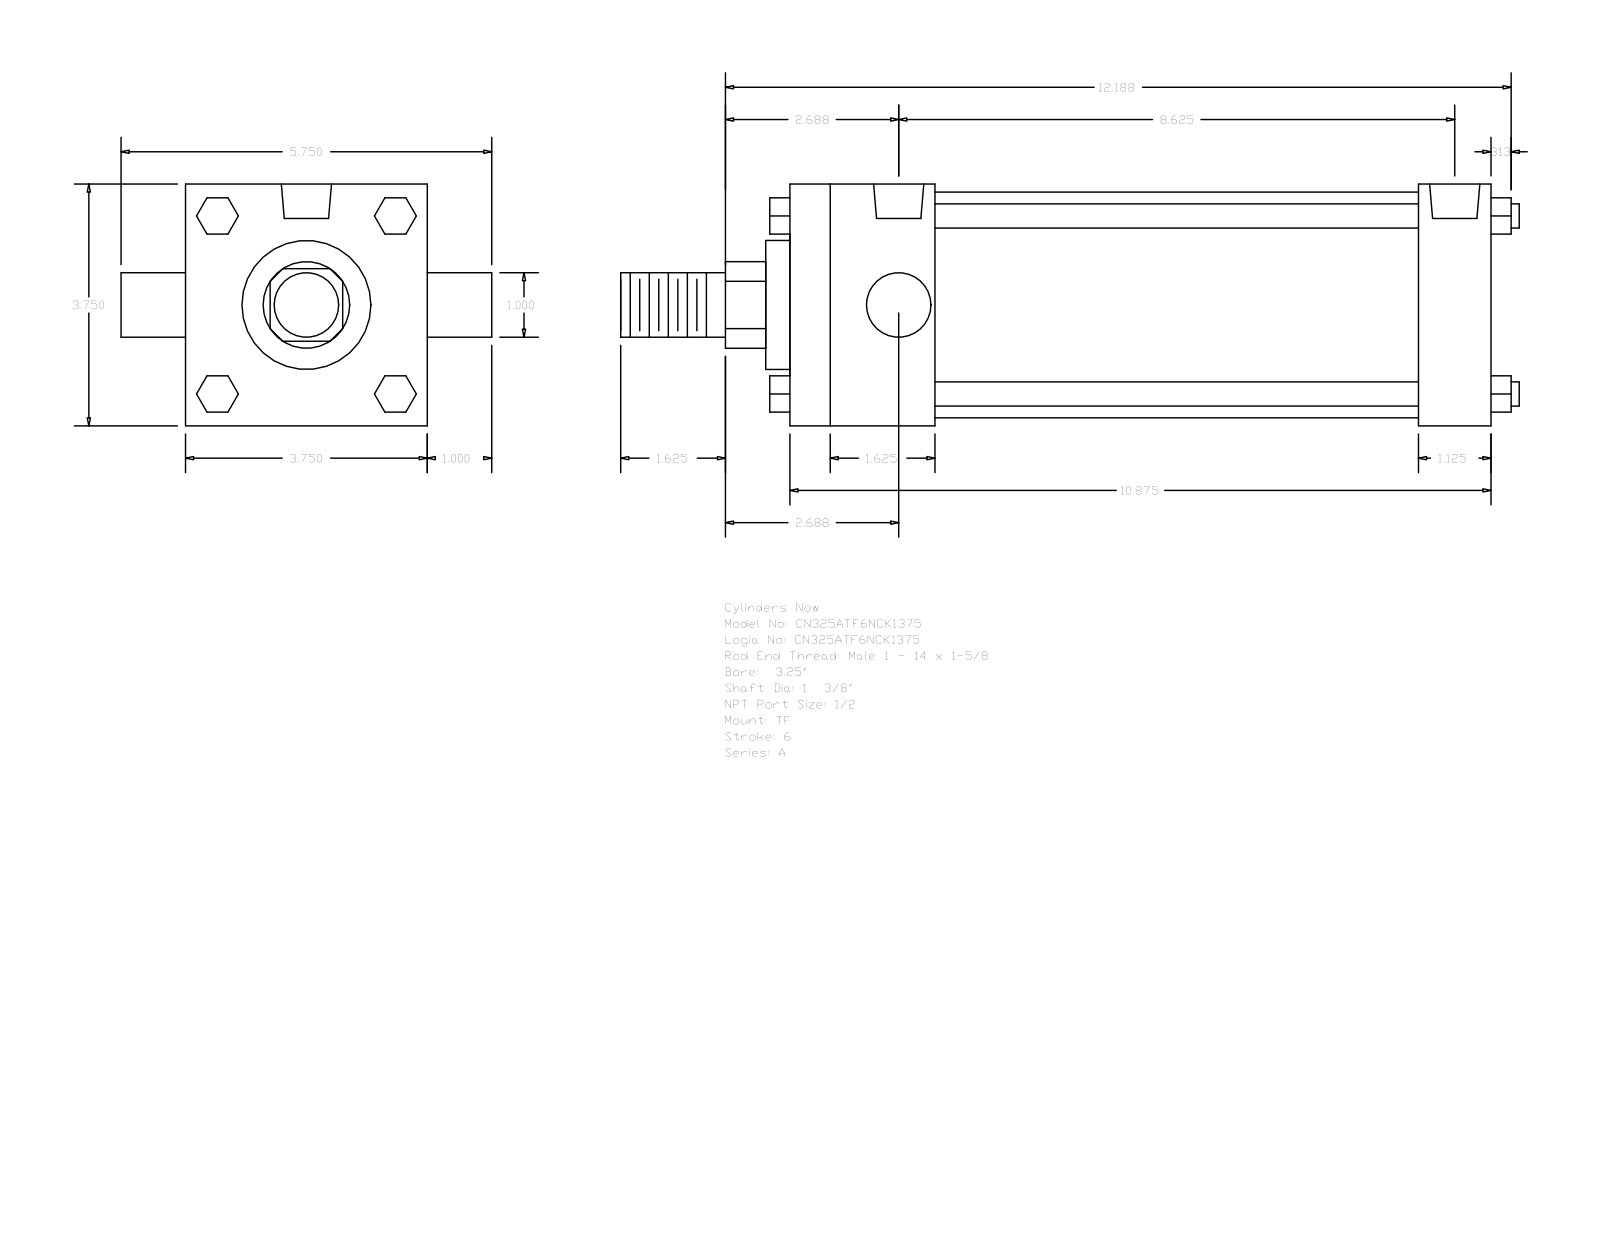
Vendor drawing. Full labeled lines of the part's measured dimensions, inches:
Part name (STEP PRODUCT): A_TF__0325_1.375
STEP written by: GSSL Pune (CONFIG_CONTROL_DESIGN)
Units: inches
Bodies: 0 solids, 120 faces (92 planar, 28 cylindrical, 0 other)
Overall size (bounding box): 13.937 × 5.75 × 3.75
Round holes (diameter × count): ⌀0.344 ×3, ⌀0.778 ×2
Round bosses / shafts (diameter × count): ⌀0.375 ×4, ⌀1 ×2, ⌀3.5 ×1, ⌀2 ×1, ⌀1.375 ×1
Partial cylindrical surfaces — rounded edges, fillets, slot ends (radius × count): R0.672 ×1
Main face-to-face distances: 3.75, 10.875, 2.25, 9.75, 7.5, 8.625, 1.125, 2.625, 0.375, 10.125
Hole centre spacings: 0.125, 8.5, 8.375, 8.625
